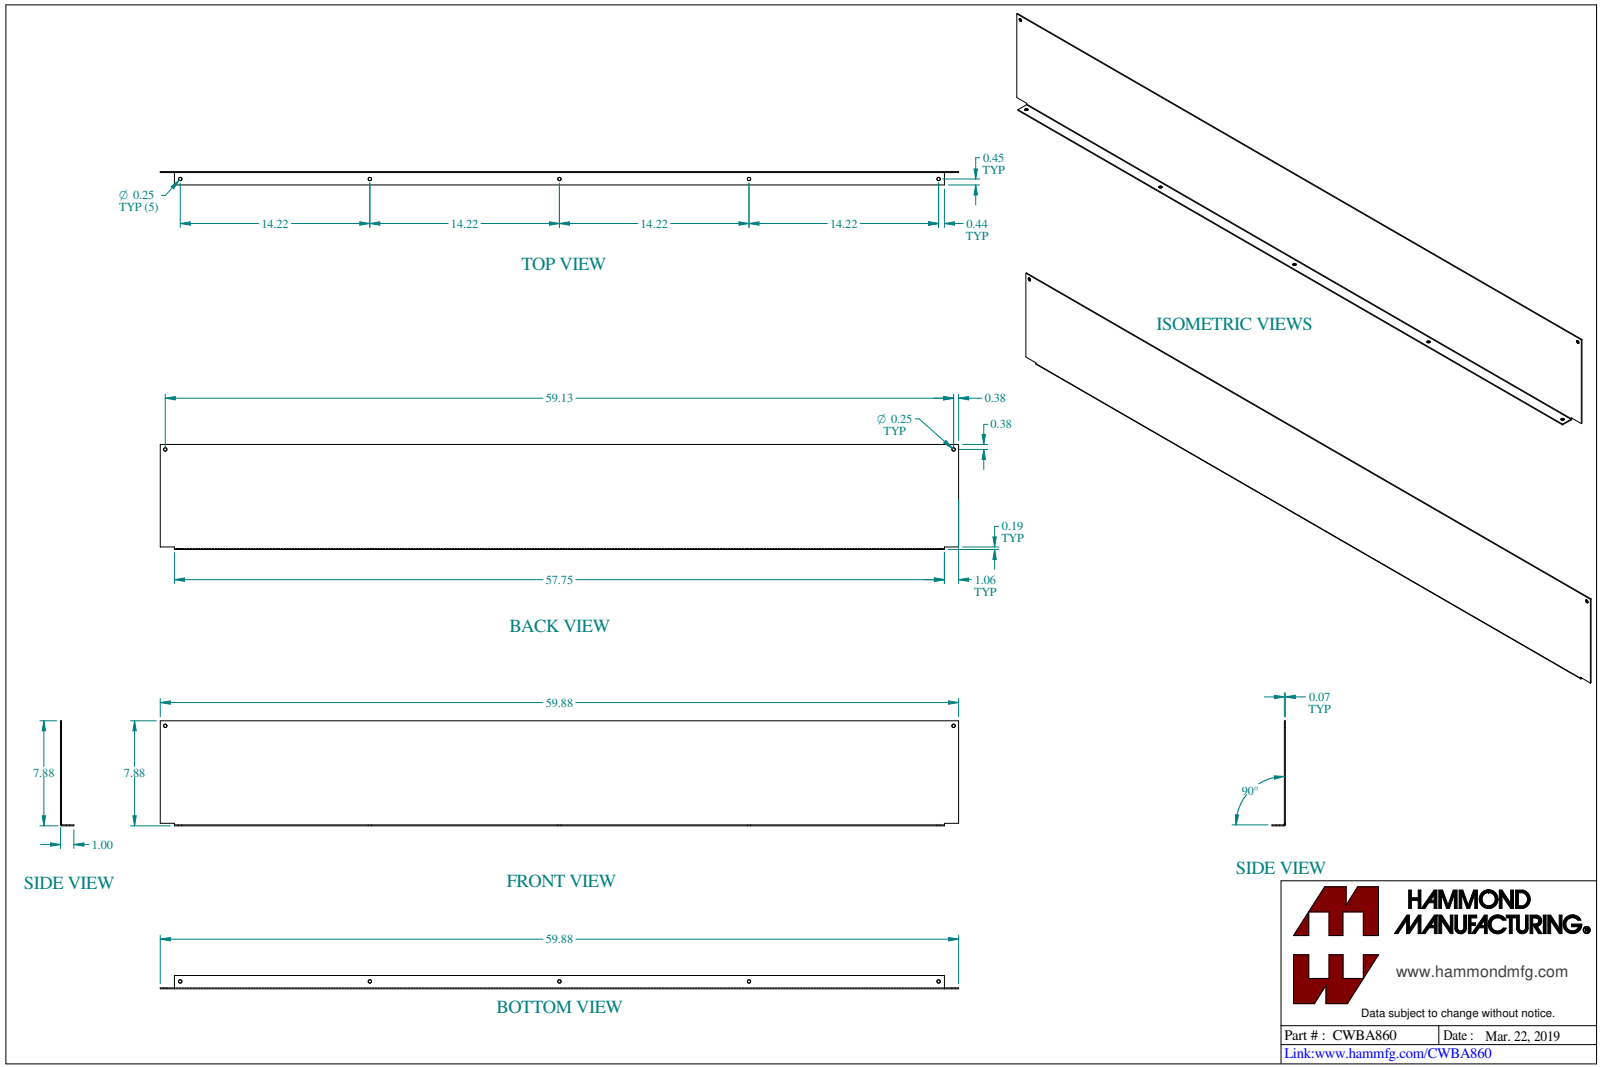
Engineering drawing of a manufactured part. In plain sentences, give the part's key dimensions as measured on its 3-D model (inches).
The part is named "CWBA860". Its 3-D file was written by "SolidWorks 2023 (CONFIG_CONTROL_DESIGN)". It is 3 solids with 63 faces: 35 planar, 22 cylindrical and 6 other. Overall it measures 59.875 by 8.303 by 1 inches. Its volume is 37.66 cubic inches and its surface area 1 056 square inches. Round holes: 7 of diameter 0.25, 1 of diameter 0.156. Round bosses or shafts: 1 of diameter 0.367, 1 of diameter 0.19. Partial cylindrical surfaces (rounded edges, fillets, slot ends): 1 of radius 0.036, 1 of radius 0.108. The main face-to-face distances are 0.072, 7.875, 7.803, 1, 0.928, 59.875, 0.187, 1.063, 58.812, 0.115. The hole center spacings are 14.219, 14.219, 28.437, 42.656, 28.438, 56.875, 59.125.
